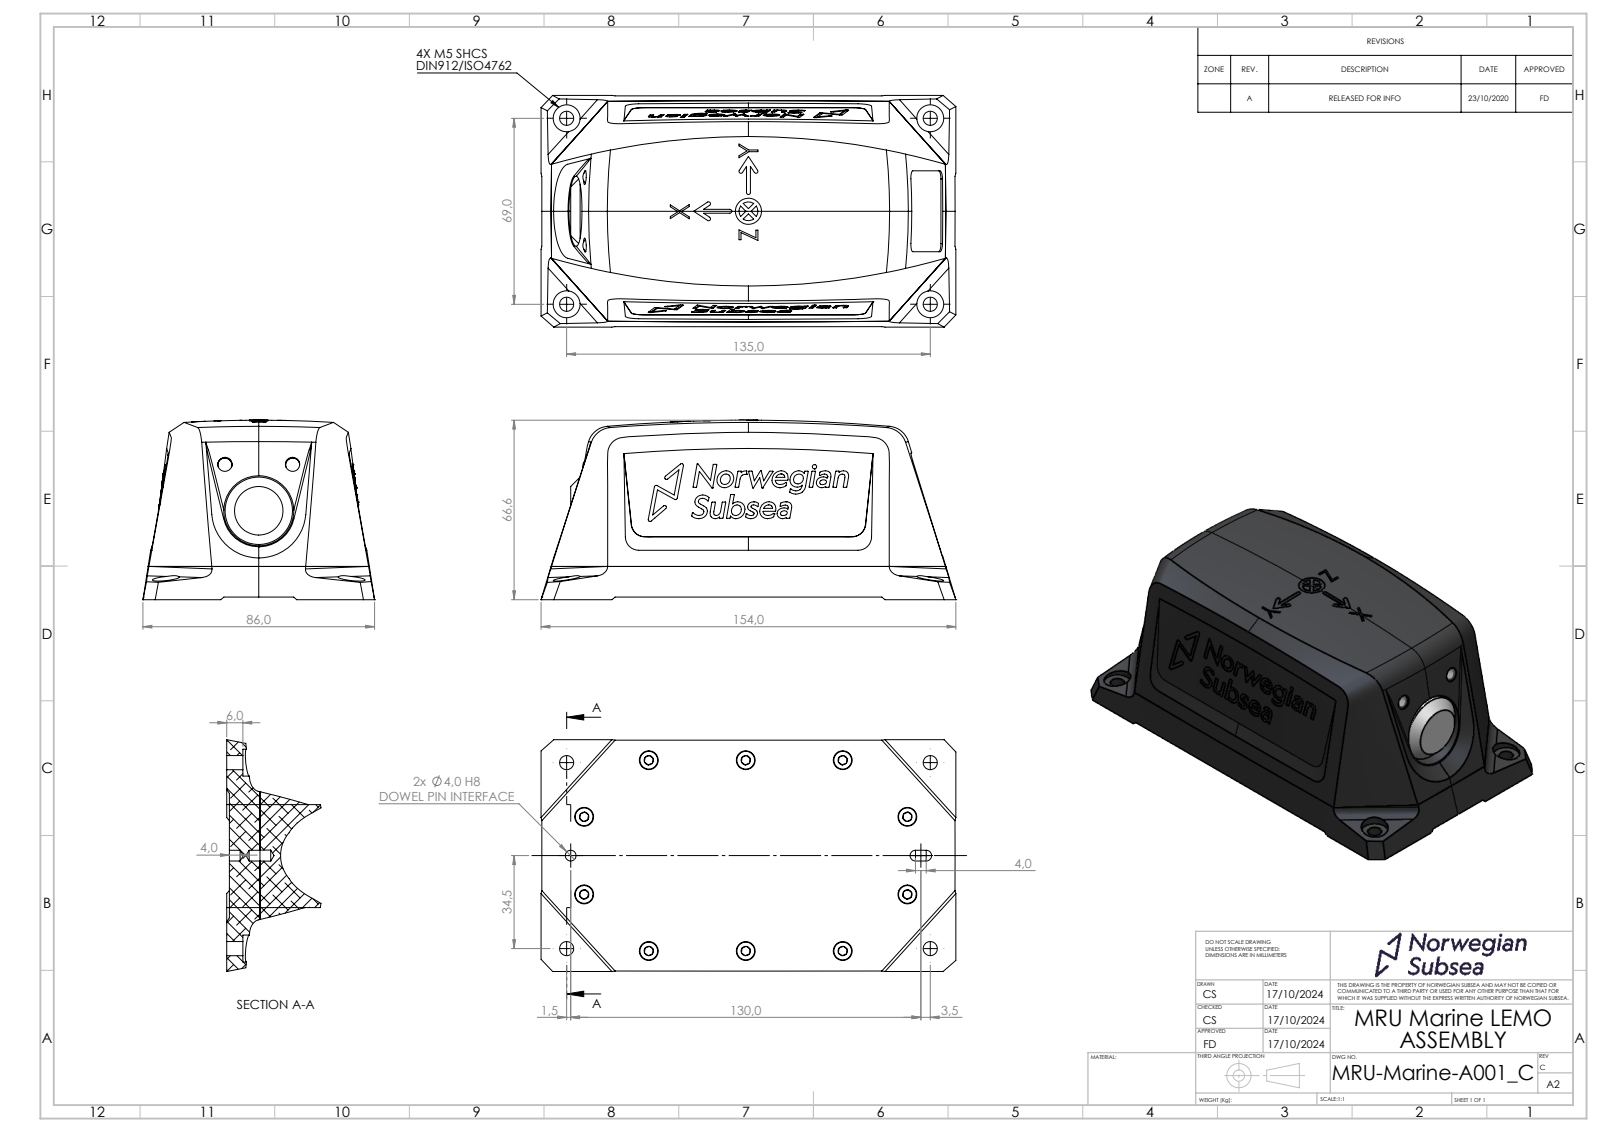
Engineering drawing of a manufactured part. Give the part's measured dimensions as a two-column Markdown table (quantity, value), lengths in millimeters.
| quantity | value |
| --- | --- |
| part name | O-RING 101.27x2.62; LEMO-2; MRU-Marine-A001_C; MRU-Marine-P001_C (+5 more) |
| STEP written by | SolidWorks 2024 (AUTOMOTIVE_DESIGN) |
| units | millimeters |
| bodies | 16 solids, 2394 faces (521 planar, 991 cylindrical, 882 other) |
| overall size | 154 × 86 × 66.61 |
| volume | 328 881 mm³ |
| surface area | 100 563 mm² |
| round holes (diameter × count) | 2.5 × 13, 0.75 × 10, 3.3 × 10, 4.2 × 10, 7 × 10, 5.2 × 7, 5.25 × 4, 10 × 4, 4 × 2, 4.1 × 2, 4.6 × 2, 5.3 × 2 |
| round bosses / shafts (diameter × count) | 4 × 12, 3.09 × 10, 1.25 × 10, 25 × 1, 15 × 1 |
| partial cylindrical surfaces (radius × count) | 0.62 × 10, 0.3 × 8, 0.85 × 8, 0.71 × 6, 4 × 6, 3 × 4, 6 × 4, 9.1 × 4 |
| main face-to-face distances | 11.35, 6, 5.35, 52.8, 58.35, 52.35, 47, 102, 1, 7 |
| hole center spacings | 69.85, 3.1, 4.38, 15.24, 41.4, 82.79, 2.36, 2.38 |
